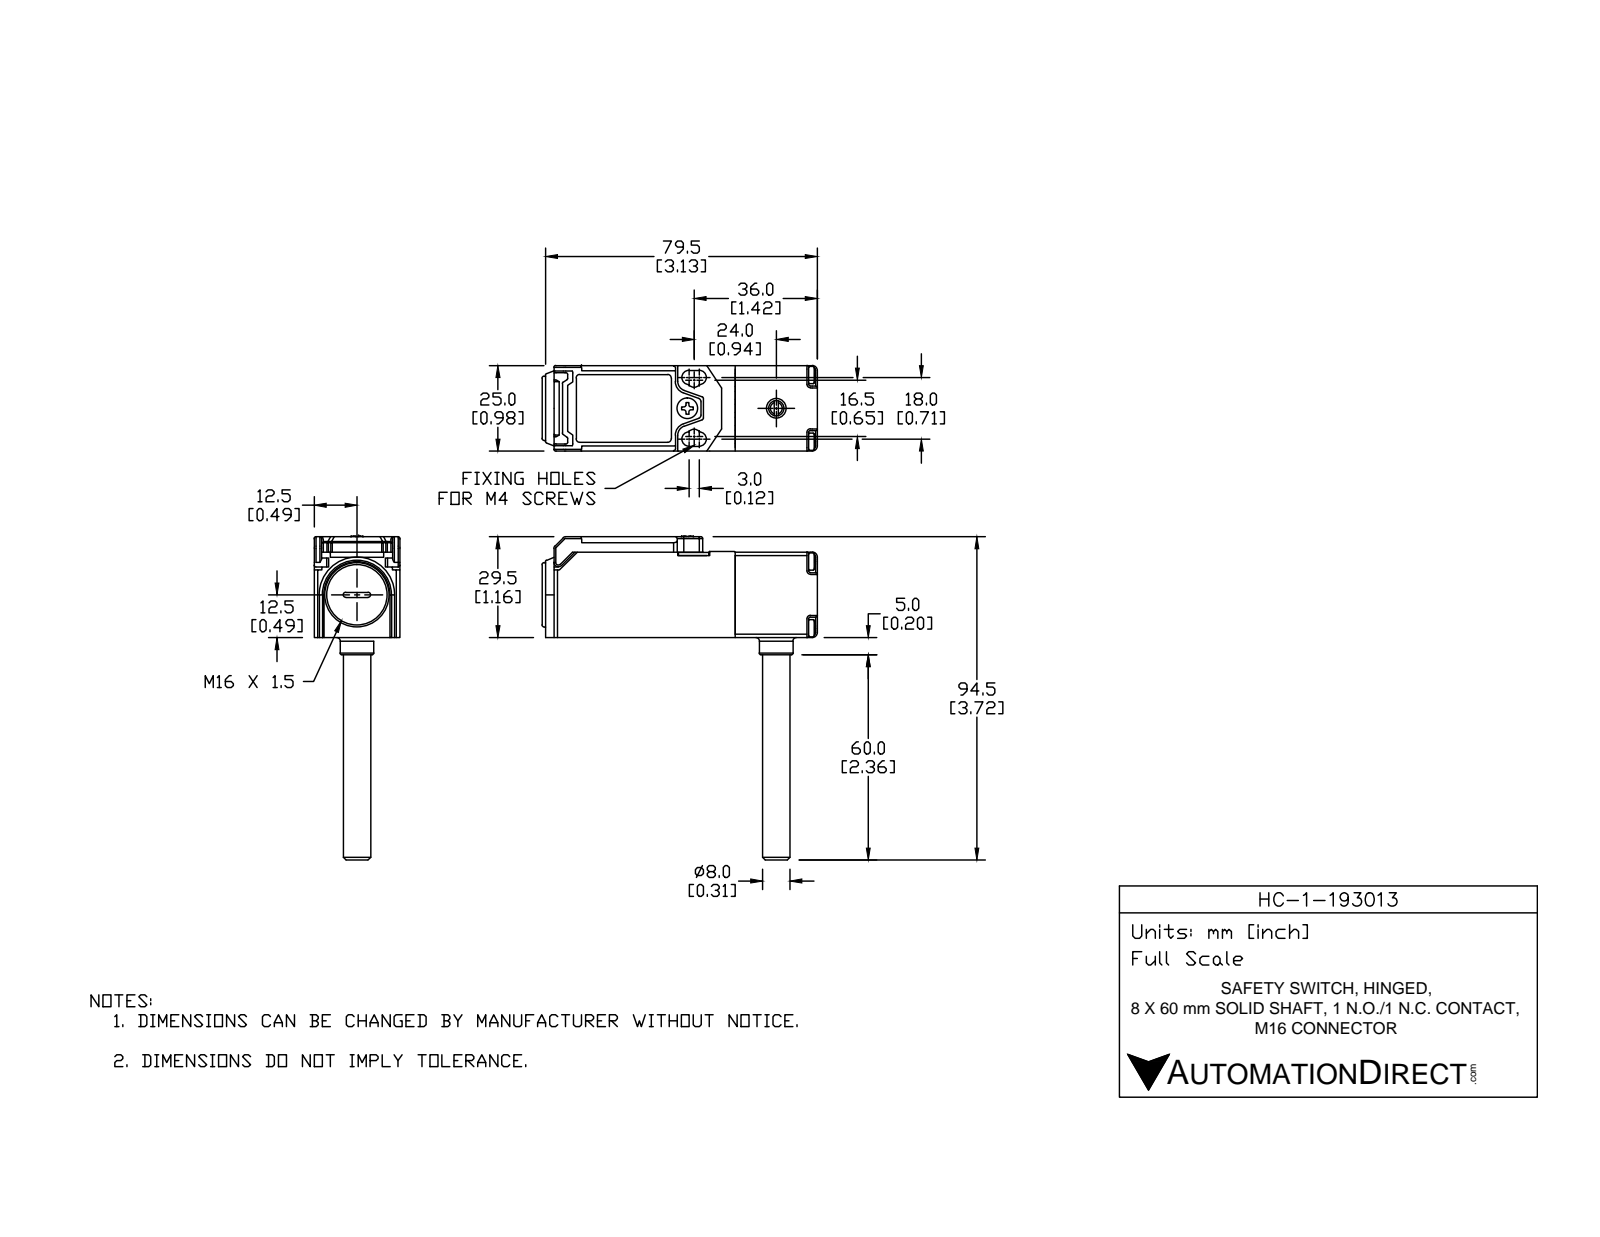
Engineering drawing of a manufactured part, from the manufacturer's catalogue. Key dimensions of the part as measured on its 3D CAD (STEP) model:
Part name (STEP PRODUCT): HC-1-193013
STEP written by: SolidWorks 2014 (AUTOMOTIVE_DESIGN)
Units: inches
Bodies: 14 solids, 1706 faces (700 planar, 601 cylindrical, 405 other)
Overall size (bounding box): 3.73 × 3.169 × 0.984
Volume: 1.733 in³ · Surface area: 42.86 in²
Round holes (diameter × count): ⌀0.126 ×5, ⌀0.094 ×4, ⌀0.059 ×2, ⌀0.063 ×2, ⌀0.071 ×2, ⌀0.087 ×2, ⌀0.142 ×2, ⌀0.055 ×1, ⌀0.081 ×1, ⌀0.098 ×1, ⌀0.102 ×1, ⌀0.185 ×1
Round bosses / shafts (diameter × count): ⌀0.102 ×5, ⌀0.197 ×4, ⌀0.079 ×4, ⌀0.138 ×2, ⌀0.74 ×1, ⌀0.531 ×1, ⌀0.386 ×1, ⌀0.315 ×1
Partial cylindrical surfaces — rounded edges, fillets, slot ends (radius × count): R0.02 ×226, R0.004 ×24, R0.012 ×20, R0.039 ×20, R0.059 ×7, R0.083 ×6, R0.11 ×6, R0.008 ×4
Main face-to-face distances: 0.984, 0.079, 0.071, 0.913, 0.039, 0.906, 0.945, 0.827, 0.874, 1.15
Hole centre spacings: 0.543, 0.768, 0.171, 0.187, 0.245, 0.414, 0.423, 0.426
